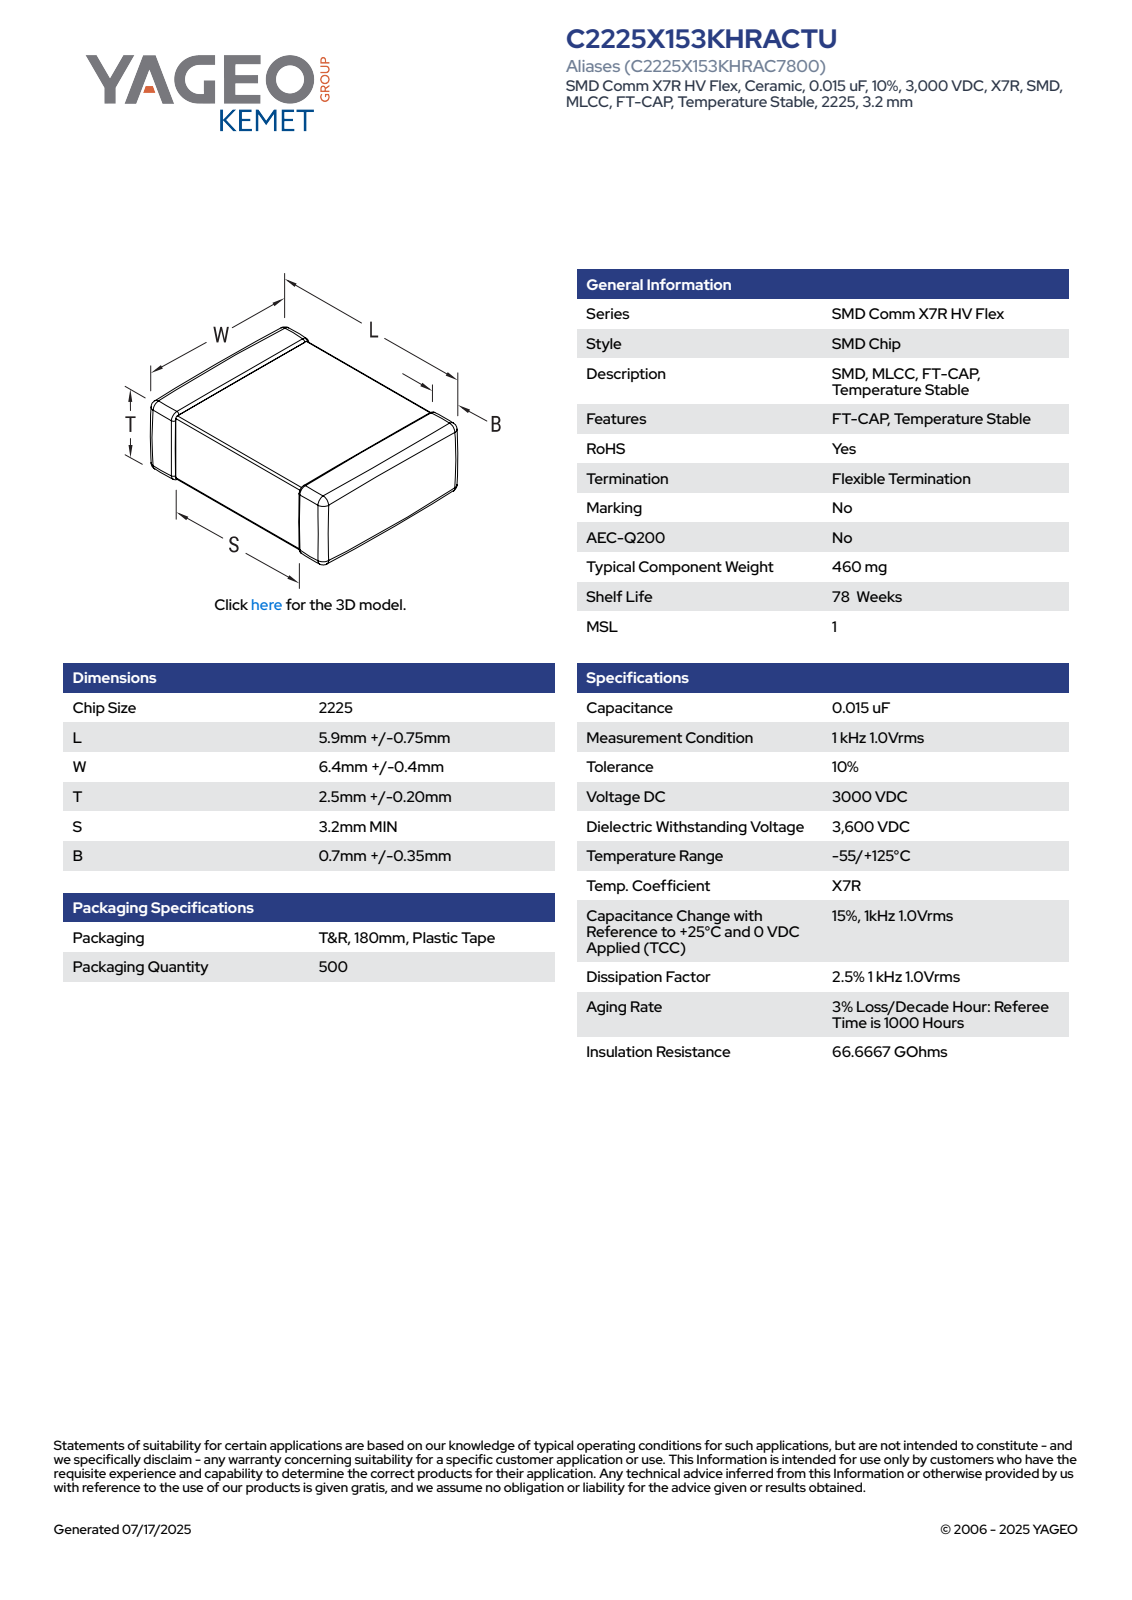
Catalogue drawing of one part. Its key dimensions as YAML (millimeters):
part_name: "CCS_CCSTDNOS_2225_L6.65W6.8T2.7B1.05"
step_written_by: "SolidWorks 2014 (AUTOMOTIVE_DESIGN)"
units: millimeters
bodies: {solids: 4, faces: 121, planar: 71, cylindrical: 34, other: 16}
overall_size: [6.8, 6.65, 2.7]
volume: 110
surface_area: 158
partial_cylinders:
  - {radius: 0.14, count: 24}
face_to_face_distances: [2.42, 2.56, 6.65, 2.7, 6.52, 6.66, 6.8, 3.29, 3.37, 0.47]
